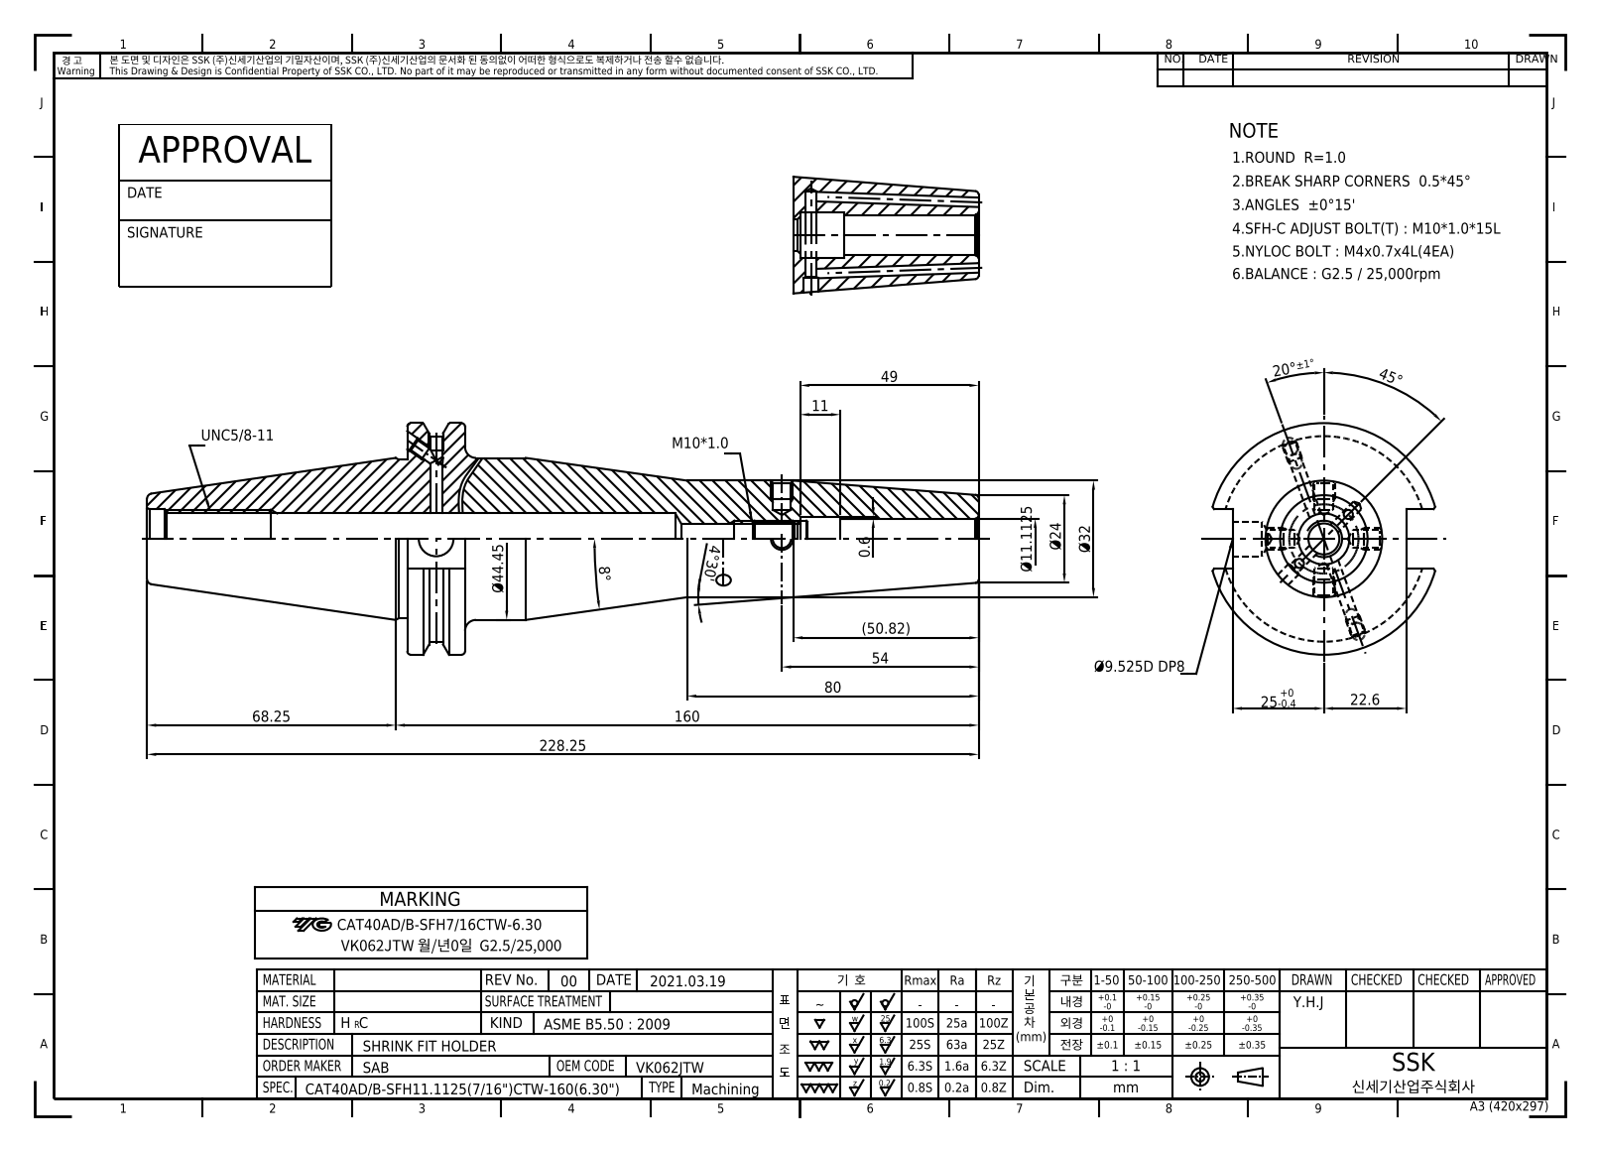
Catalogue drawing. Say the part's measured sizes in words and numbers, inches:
The part is named "LO-CAT40ADB-SFH11.1125CTW-160". Its 3-D file was written by "Autodesk Inventor 2024 (AUTOMOTIVE_DESIGN)". It is 1 solid with 91 faces: 37 planar, 32 cylindrical and 22 other. Overall it measures 8.986 by 2.5 by 2.405 inches. Its volume is 13.3 cubic inches and its surface area 62.52 square inches. Round holes: 4 of diameter 0.128, 2 of diameter 0.079, 2 of diameter 0.157, 2 of diameter 0.165, 1 of diameter 0.33, 1 of diameter 0.375, 1 of diameter 0.437, 1 of diameter 0.485, 1 of diameter 0.512, 1 of diameter 0.527, 1 of diameter 0.642. Round bosses or shafts: 1 of diameter 2.5, 1 of diameter 1.75, 1 of diameter 1.717, 1 of diameter 1.26. Partial cylindrical surfaces (rounded edges, fillets, slot ends): 1 of radius 1.108. The main face-to-face distances are 0.625, 6.174, 5.549, 1.874, 0.645, 2.812, 3.437, 8.986, 3.05, 0.238.
